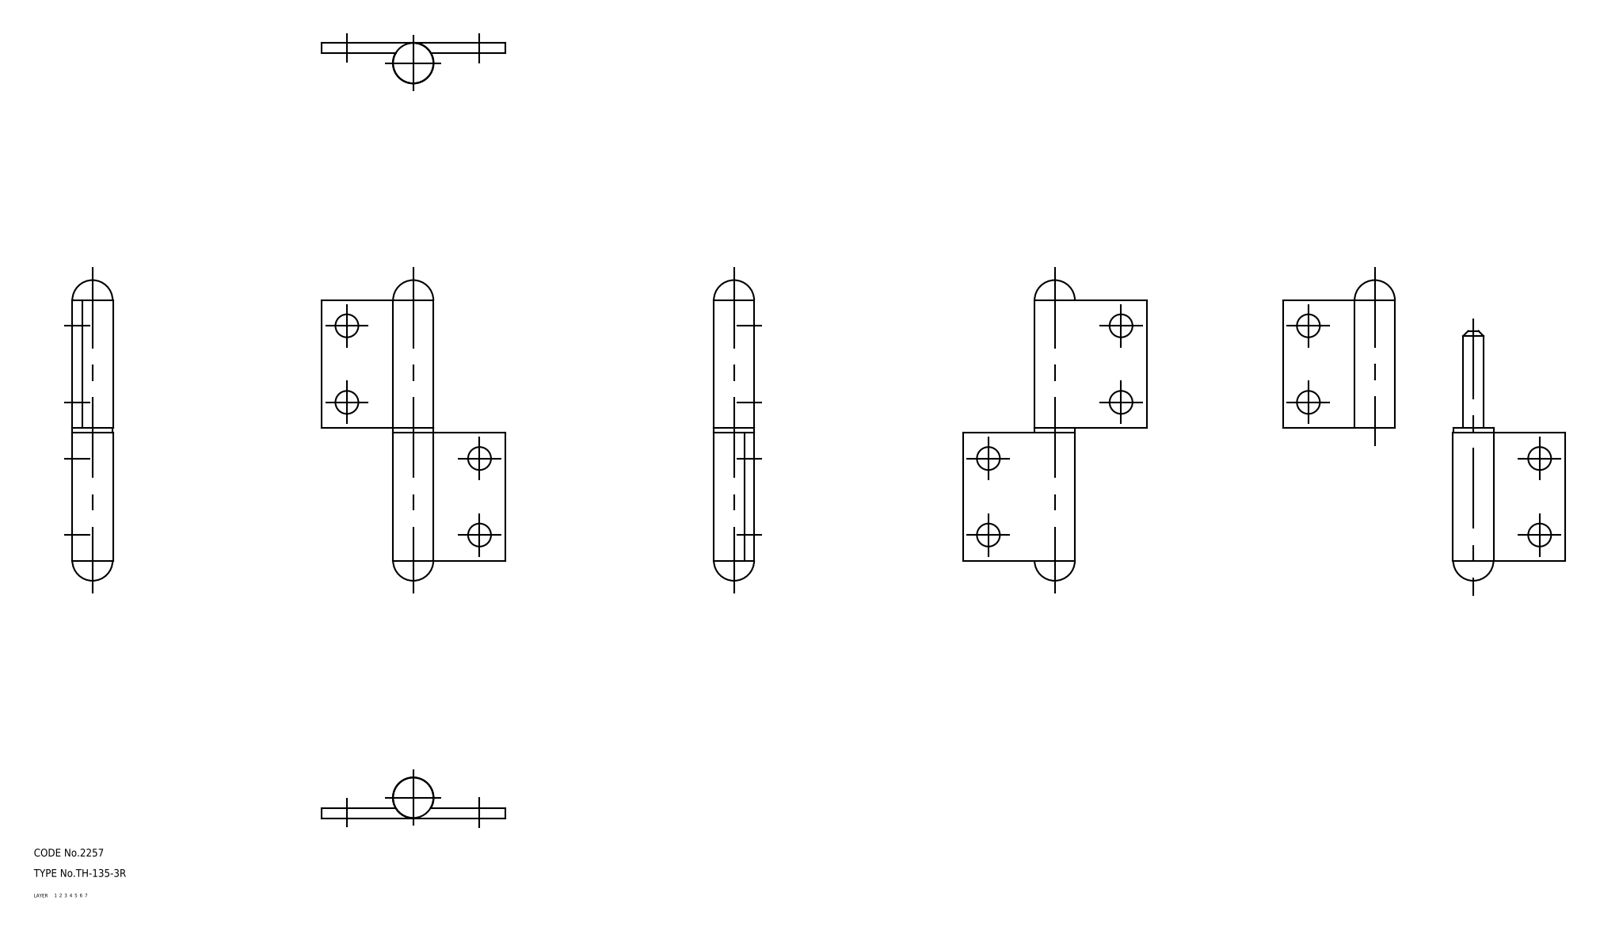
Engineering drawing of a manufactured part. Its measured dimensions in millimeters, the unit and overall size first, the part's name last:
Units: millimetres
Overall size (bounding box): 117.77 × 72 × 16
Volume: 33 034 mm³ · Surface area: 19 478 mm²
Bodies: 6 solids, 44 faces (0 planar, 0 cylindrical, 44 other)
Part name (STEP PRODUCT): cap; washer; shaft; hinge piece_B (+2 more)
STEP written by: CADfix (AUTOMOTIVE_DESIGN)
